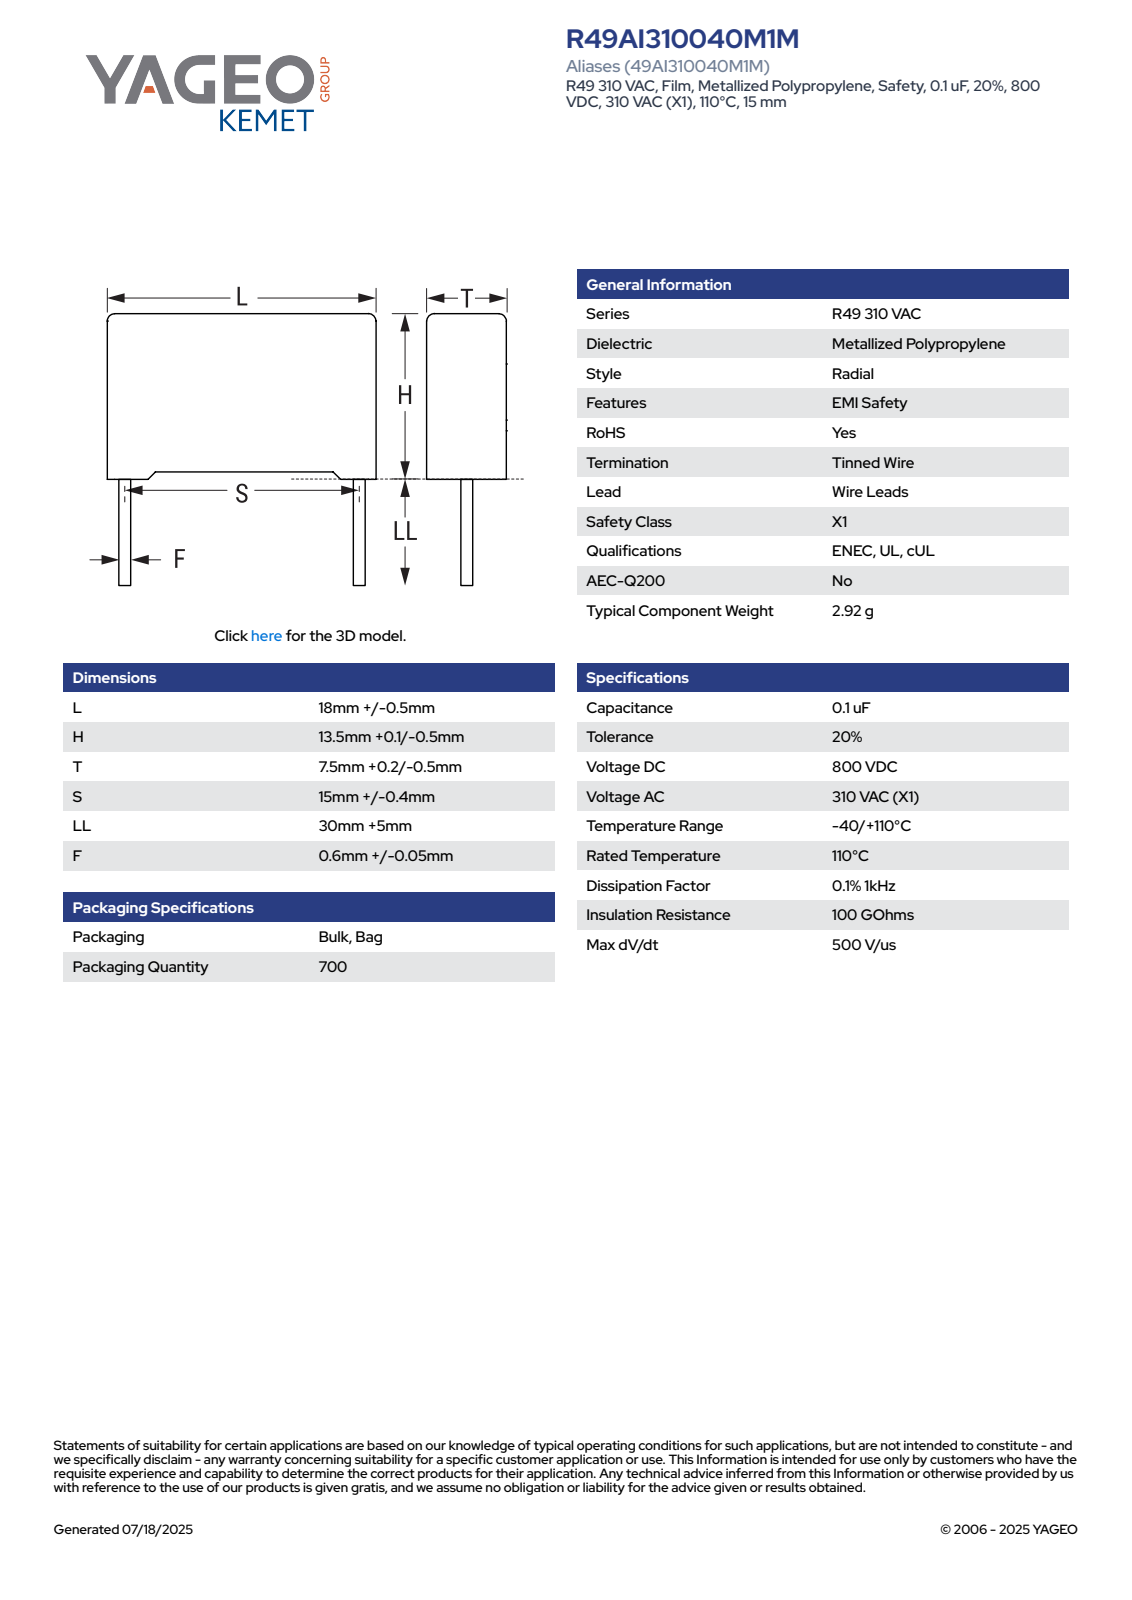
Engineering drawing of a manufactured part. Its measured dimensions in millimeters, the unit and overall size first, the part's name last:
Units: millimetres
Overall size (bounding box): 48.6 × 18.5 × 7.71
Round bosses / shafts (diameter × count): ⌀0.65 ×2
Partial cylindrical surfaces — rounded edges, fillets, slot ends (radius × count): R0.5 ×4
Main face-to-face distances: 7.7, 12.85, 18.5, 0.62, 0.75, 13.6, 7.08, 0.47, 13.13, 17.88
Volume: 1 868 mm³ · Surface area: 1 172 mm²
Bodies: 4 solids, 85 faces (77 planar, 8 cylindrical, 0 other)
Part name (STEP PRODUCT): CFR_RB2_18X13.5X7.5_L18.5H13.6T7.7S15LL35F0.65
STEP written by: SolidWorks 2021 (AUTOMOTIVE_DESIGN)
